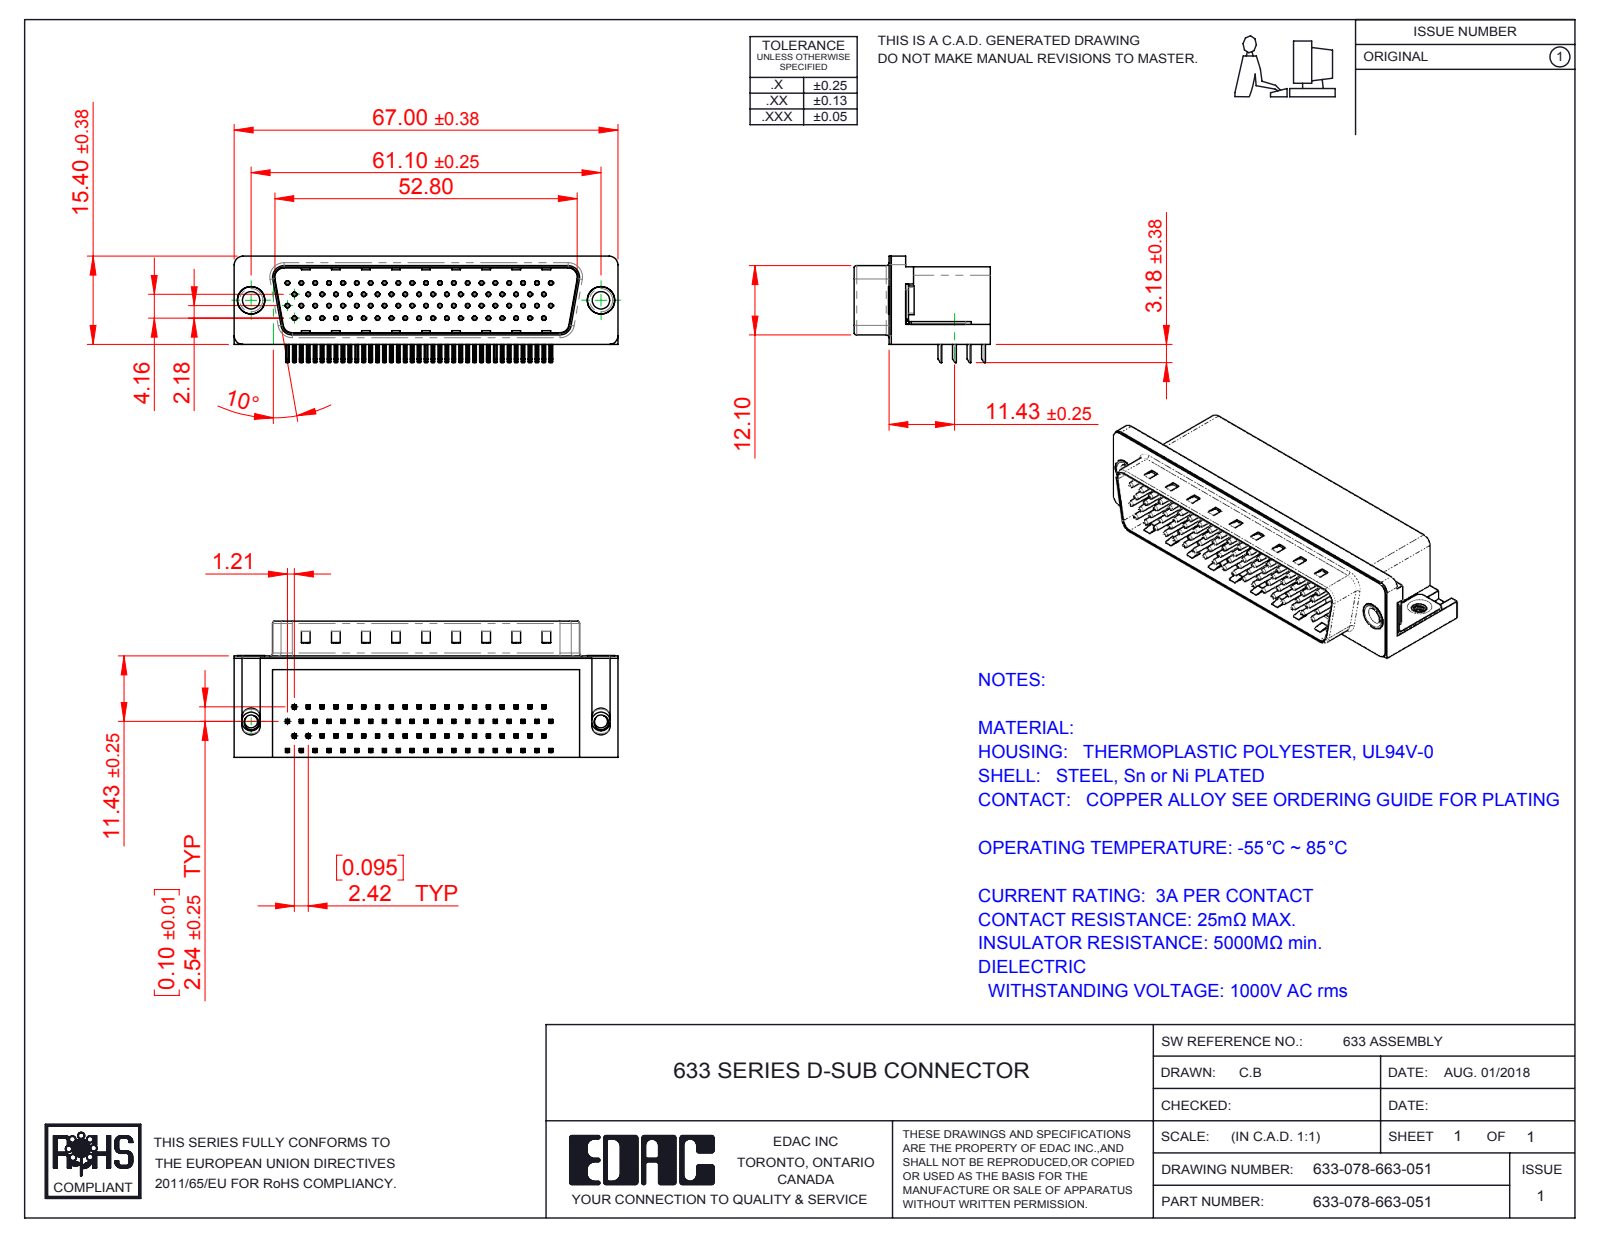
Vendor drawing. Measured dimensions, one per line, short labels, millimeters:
name: 633 Contact Top_78 Contact; 633 4-40 Threaded Board Mount_78 Contact; 633 Contact Top 78; 633-078-663-051 (+5 more)
written by: SolidWorks 2016 (CONFIG_CONTROL_DESIGN)
unit: mm
bodies: 84 solids, 6266 faces (3981 planar, 1772 cylindrical, 513 other)
size: 67 × 23.8 × 18.58
volume: 14 613 mm³; area: 16 409 mm²
holes: 78× ⌀0.35, 78× ⌀0.8, 2× ⌀2.26, 2× ⌀3.05, 2× ⌀4, 2× ⌀4.8, 2× ⌀5
bosses: 78× ⌀0.75, 2× ⌀4.9, 2× ⌀4.75, 2× ⌀3.85, 2× ⌀3.26
rounds: 320× R0.25, 156× R0.12, 16× R1, 9× R0.5, 8× R1.6, 6× R1.5, 4× R0.45, 4× R0.9
face distances: 0.4, 13.2, 17.3, 11.7, 13.35, 2.05, 13.75, 1.65, 1.85, 11.9
hole spacings: 2.42, 4.84, 7.26, 9.68, 6.26, 7.13, 12.1, 8.62
